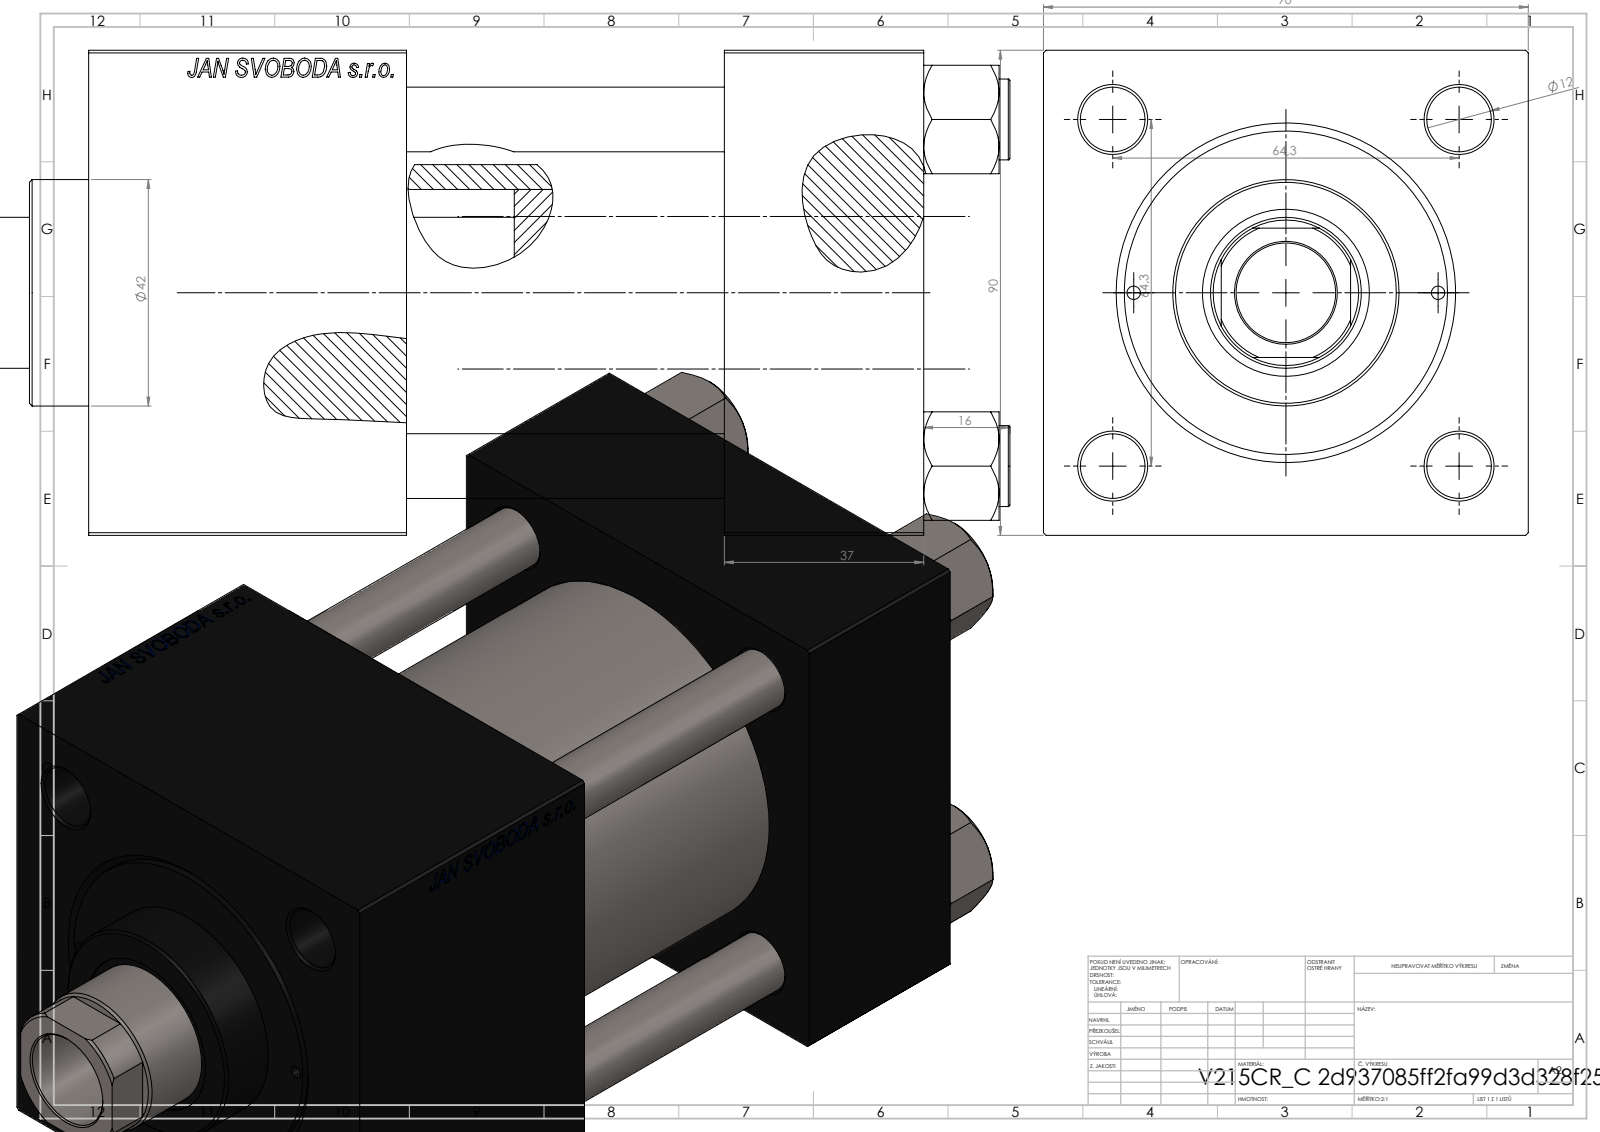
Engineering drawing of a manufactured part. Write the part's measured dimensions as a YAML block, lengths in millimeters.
part_name: "V215_VC_A; V215CR_VCP_C; V215CR_C_TYCINKA; V215CR_C_Body (+1 more)"
step_written_by: "SolidWorks 2019 (CONFIG_CONTROL_DESIGN)"
units: millimeters
bodies: {solids: 11, faces: 1154, planar: 528, cylindrical: 90, other: 536}
overall_size: [203, 90, 90]
volume: 946836
surface_area: 179207
round_holes:
  - {diameter: 12, count: 4}
  - {diameter: 2.5, count: 2}
  - {diameter: 7, count: 2}
  - {diameter: 20.96, count: 2}
  - {diameter: 30, count: 2}
  - {diameter: 18.5, count: 1}
  - {diameter: 28, count: 1}
  - {diameter: 31, count: 1}
  - {diameter: 50, count: 1}
  - {diameter: 60, count: 1}
  - {diameter: 63, count: 1}
round_bosses_or_shafts:
  - {diameter: 15, count: 4}
  - {diameter: 69, count: 1}
  - {diameter: 42, count: 1}
partial_cylinders:
  - {radius: 13.5, count: 1}
face_to_face_distances: [90, 59, 37, 155, 118, 96, 126.3, 89.3, 30.3, 28.7]
hole_center_spacings: [32.39, 45.47, 64.3, 68.42, 28.25, 90.93, 56.5, 97.5]
